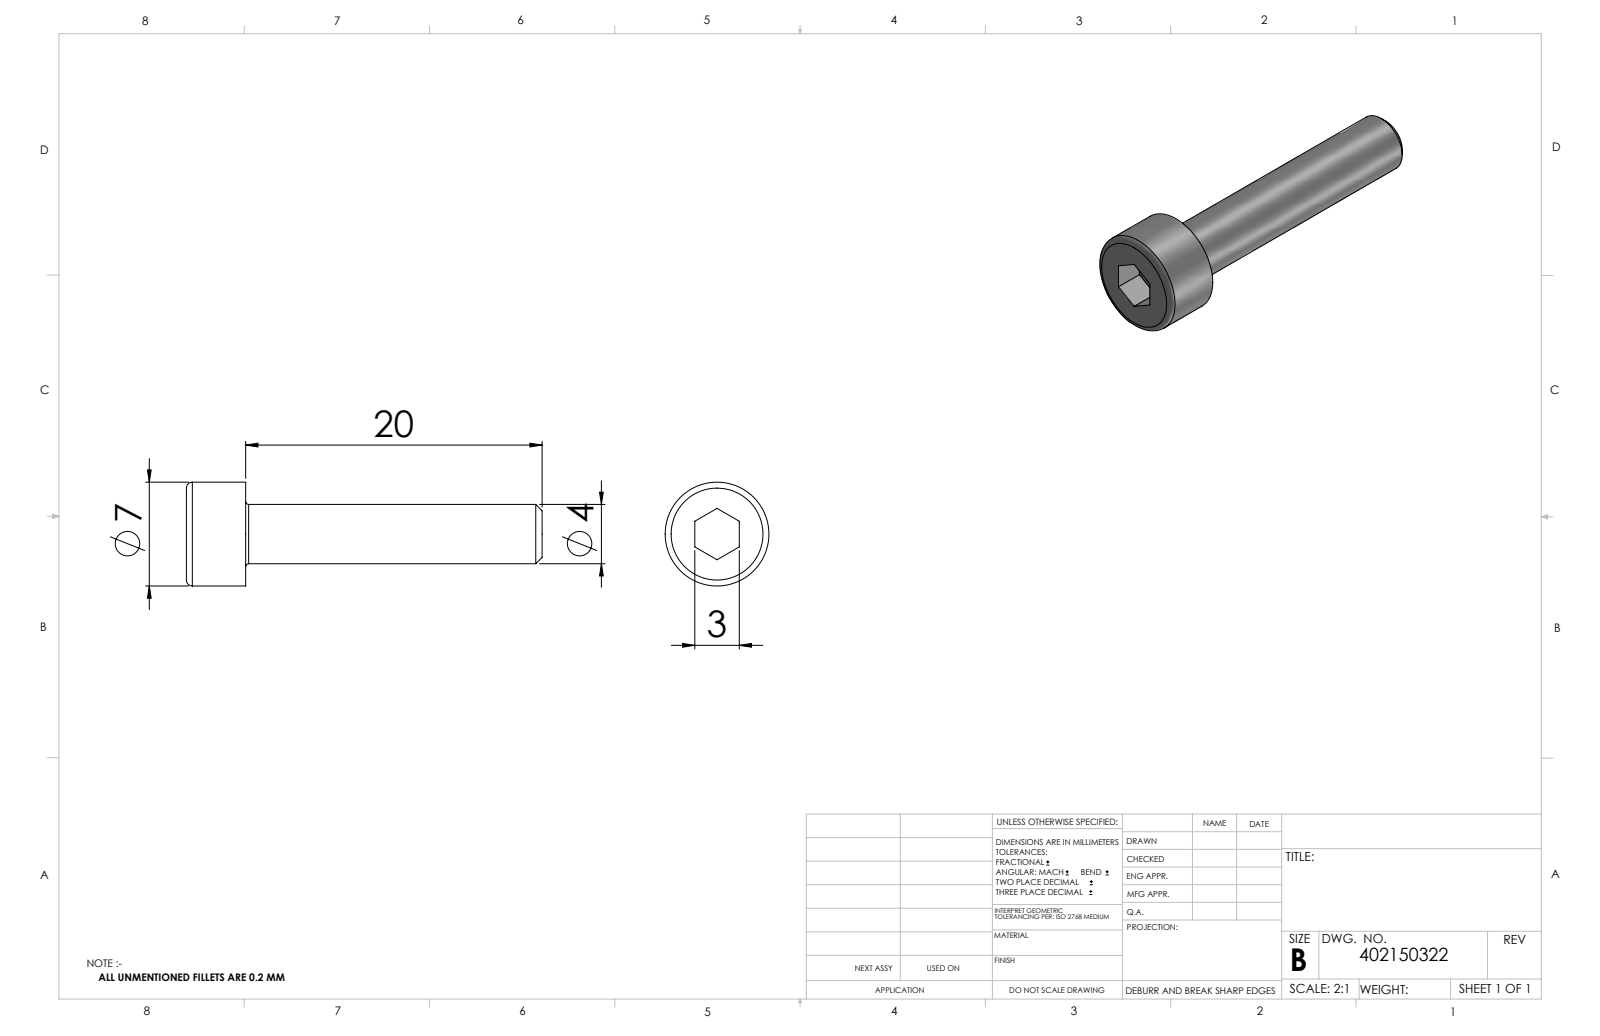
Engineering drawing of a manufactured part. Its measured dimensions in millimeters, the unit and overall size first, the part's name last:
Units: millimetres
Overall size (bounding box): 24 × 7 × 7
Round bosses / shafts (diameter × count): ⌀7 ×1, ⌀4 ×1
Main face-to-face distances: 4, 2, 3, 24, 22, 20
Volume: 388 mm³ · Surface area: 429 mm²
Bodies: 1 solid, 20 faces (10 planar, 4 cylindrical, 6 other)
Part name (STEP PRODUCT): 402150322_c_1
STEP written by: SolidWorks 2014 (CONFIG_CONTROL_DESIGN)
